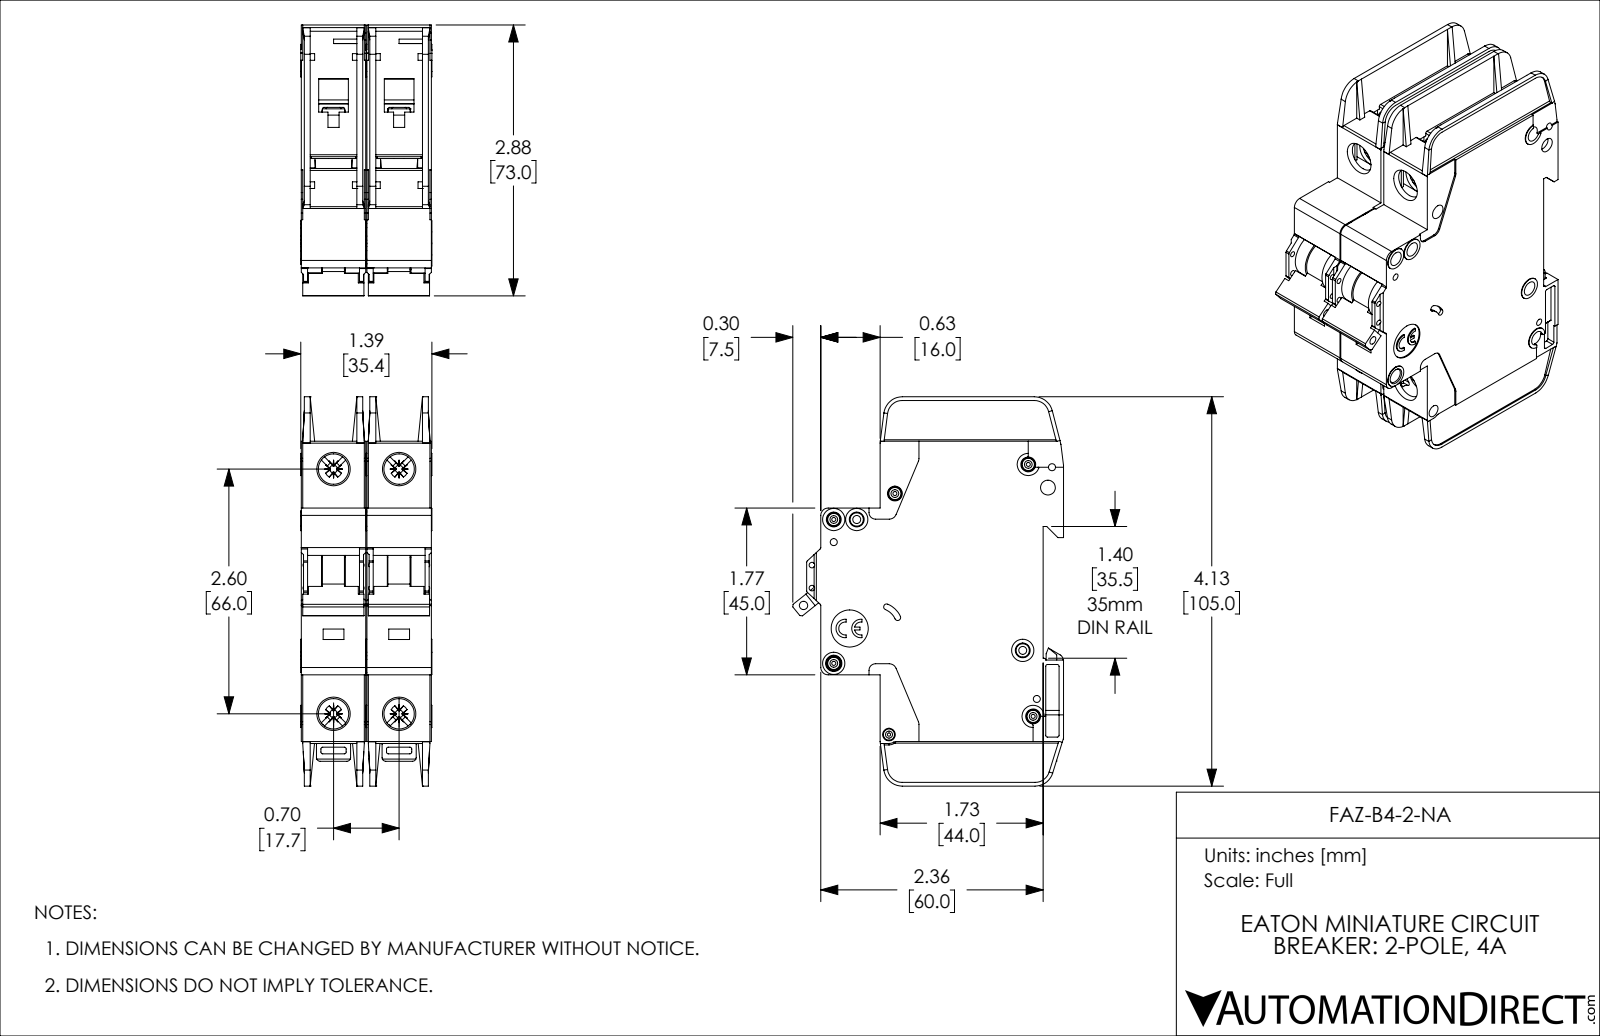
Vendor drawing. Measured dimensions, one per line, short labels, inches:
name: FAZ-B4-2-NA
written by: SolidWorks 2019 (AUTOMOTIVE_DESIGN)
unit: in
bodies: 2 solids, 2254 faces (1342 planar, 714 cylindrical, 198 other)
size: 4.134 × 2.876 × 1.394
volume: 9.365 in³; area: 82.01 in²
holes: 8× ⌀0.157, 5× ⌀0.043, 4× ⌀0.075, 4× ⌀0.323, 2× ⌀0.059, 2× ⌀0.085, 1× ⌀0.035, 1× ⌀0.089, 1× ⌀0.098, 1× ⌀0.134, 1× ⌀0.394
bosses: 5× ⌀0.13, 4× ⌀0.236, 3× ⌀0.118, 2× ⌀0.098
rounds: 57× R0.02, 20× R0.016, 14× R0.039, 10× R0.079, 8× R0.043, 5× R0.008, 5× R0.197, 4× R0.01
face distances: 0.697, 0.047, 0.685, 0.591, 0.094, 0.638, 0.543, 1.382, 0.744, 0.65
hole spacings: 0.244, 0.537, 0.697, 0.87, 2.598, 2.69, 0.189, 0.199
